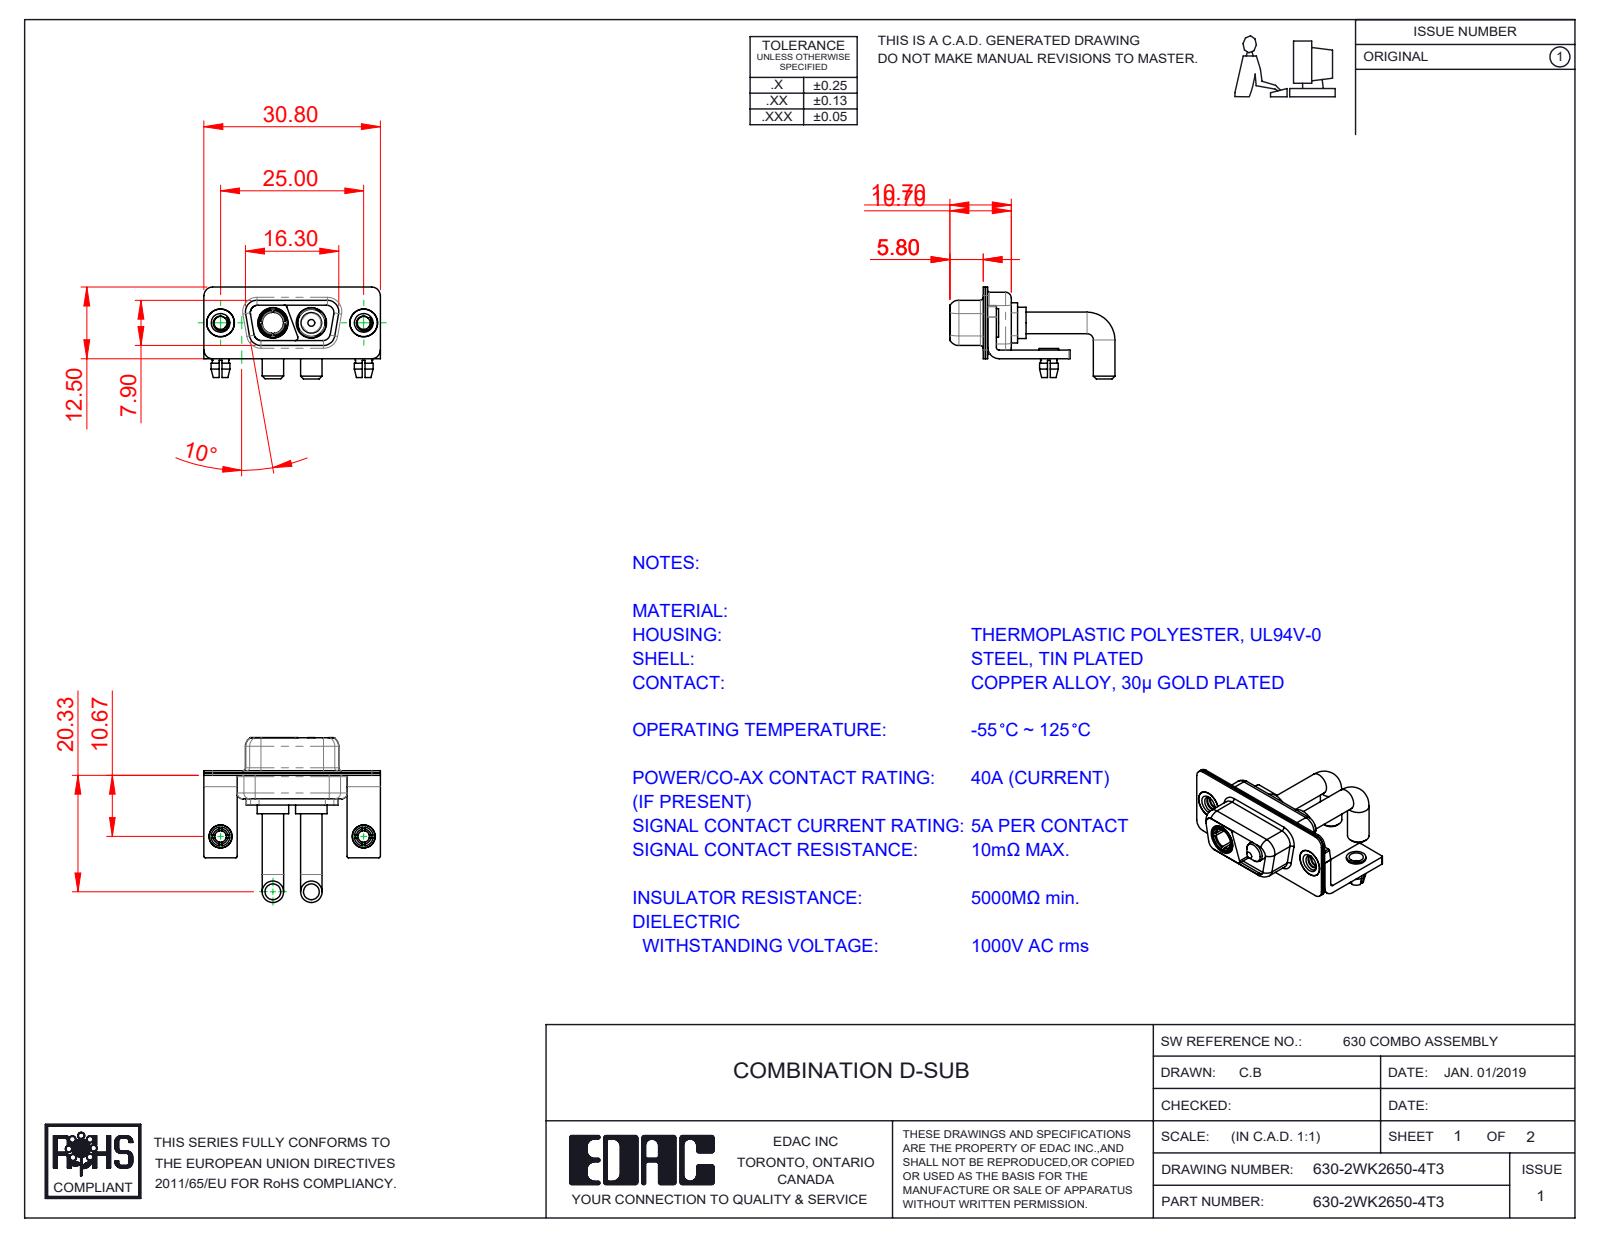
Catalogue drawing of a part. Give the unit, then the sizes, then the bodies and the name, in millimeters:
Units: millimetres
Overall size (bounding box): 30.8 × 28.8 × 16.05
Round holes (diameter × count): ⌀4.85 ×4, ⌀2 ×2, ⌀2.26 ×2, ⌀2.5 ×2, ⌀3.2 ×2, ⌀4 ×2, ⌀4.05 ×2, ⌀5.3 ×2, ⌀3.7 ×1
Round bosses / shafts (diameter × count): ⌀3.75 ×4, ⌀5.5 ×2, ⌀5.2 ×2, ⌀5 ×2, ⌀4.95 ×2, ⌀4.8 ×2, ⌀4.75 ×2, ⌀4 ×2
Partial cylindrical surfaces — rounded edges, fillets, slot ends (radius × count): R0.25 ×16, R1.5 ×16, R2 ×13, R1.35 ×8, R1.6 ×8, R0.5 ×7, R0.6 ×4, R0.65 ×4
Main face-to-face distances: 0.4, 1.5, 0.8, 1.4, 0.45, 1.8, 8.45, 2.3, 8.9, 1.35
Hole centre spacings: 9.14, 15.86, 25, 6.72
Volume: 2 304 mm³ · Surface area: 5 154 mm²
Bodies: 13 solids, 533 faces (174 planar, 234 cylindrical, 125 other)
Part name (STEP PRODUCT): 630-2WK2650-4T3; 630Combo Threaded Rivet_3; Power Socket_Ext 40A RA; 630Combo Shell Front_09 Contacts (+5 more)
STEP written by: SolidWorks 2020 (CONFIG_CONTROL_DESIGN)
